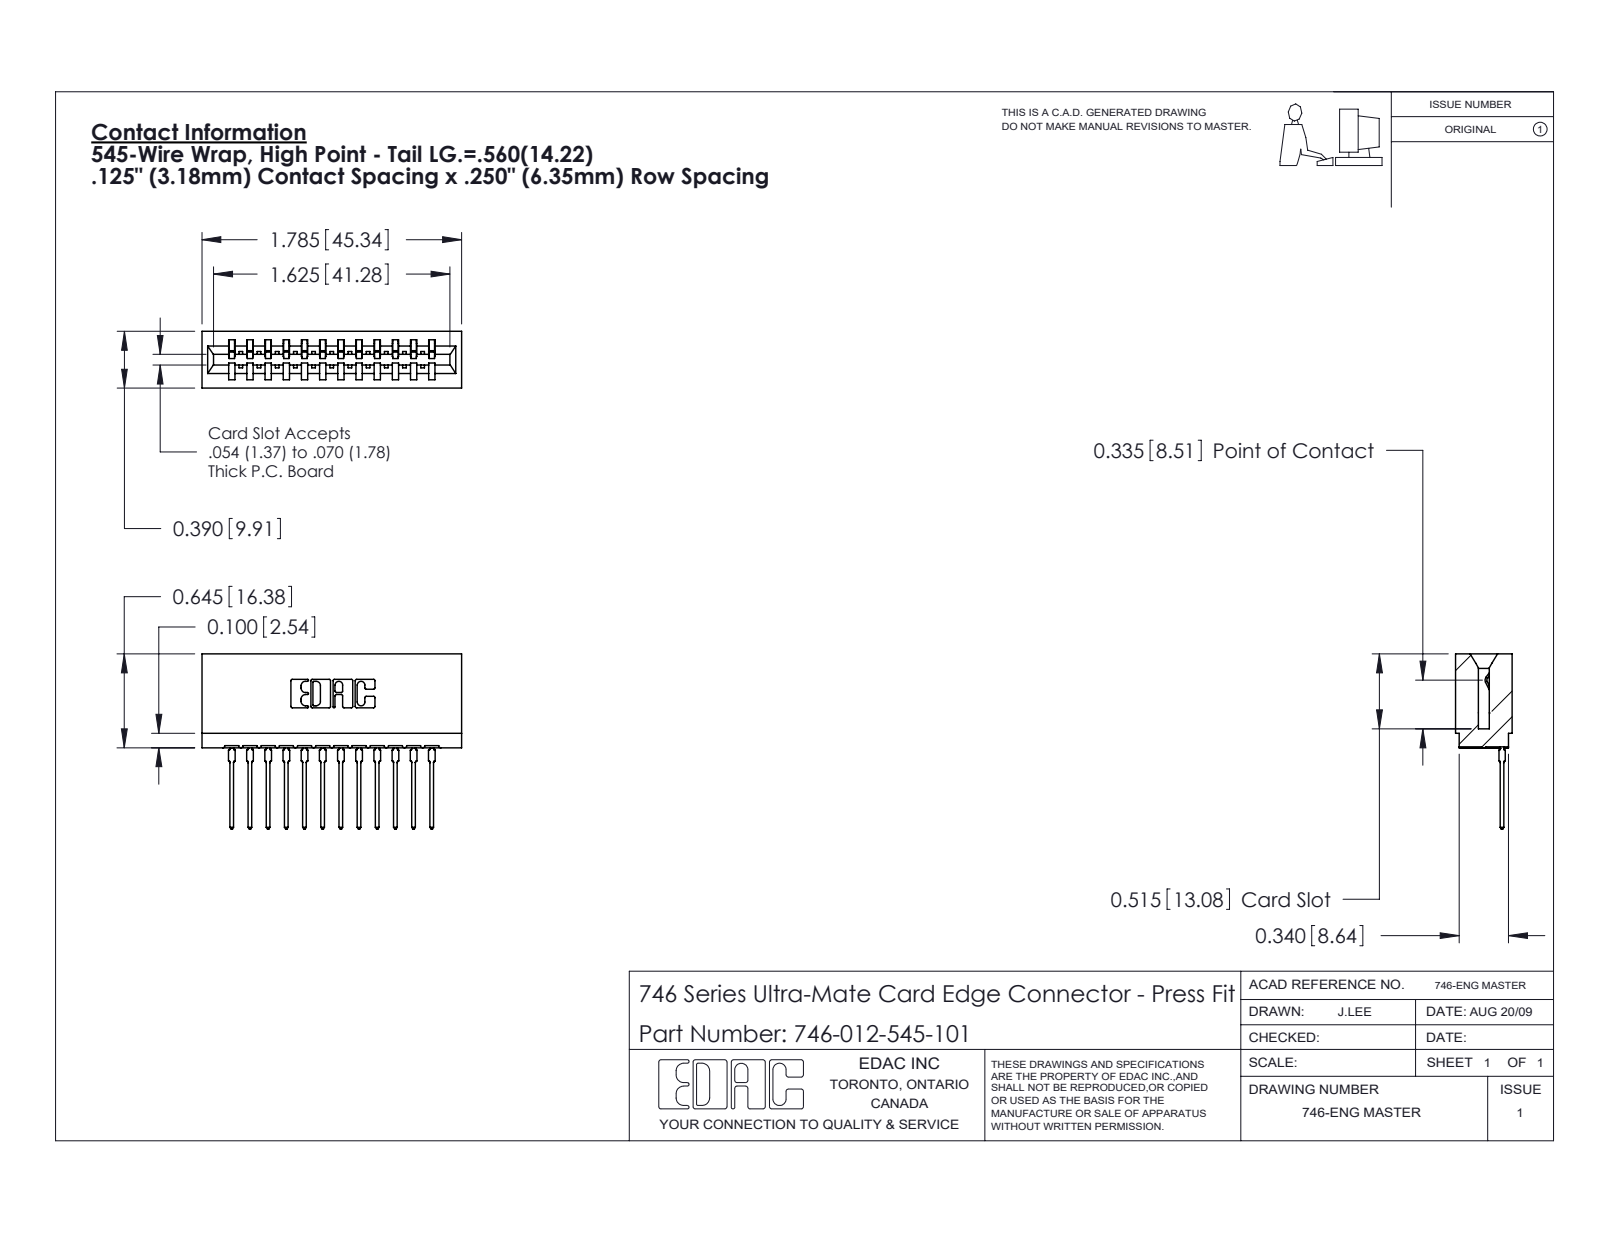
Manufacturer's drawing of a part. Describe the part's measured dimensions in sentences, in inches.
The part is named "746-012-545-101; 746 Part_.515 Slot Depth - 01; 746-292-001_545". Its 3-D file was written by "SolidWorks 2020 (CONFIG_CONTROL_DESIGN)". It is 13 solids with 1393 faces: 811 planar, 270 cylindrical and 312 other. Overall it measures 1.785 by 1.204 by 0.39 inches. Its volume is 0.304 cubic inches and its surface area 10.91 square inches. Partial cylindrical surfaces (rounded edges, fillets, slot ends): 24 of radius 0.021, 22 of radius 0.01, 13 of radius 0.015, 6 of radius 0.007, 6 of radius 0.031, 4 of radius 0.005, 4 of radius 0.011, 3 of radius 0.026. The main face-to-face distances are 0.25, 0.333, 0.5, 0.057, 0.125, 0.125, 0.39, 0.042, 0.208, 0.292.
